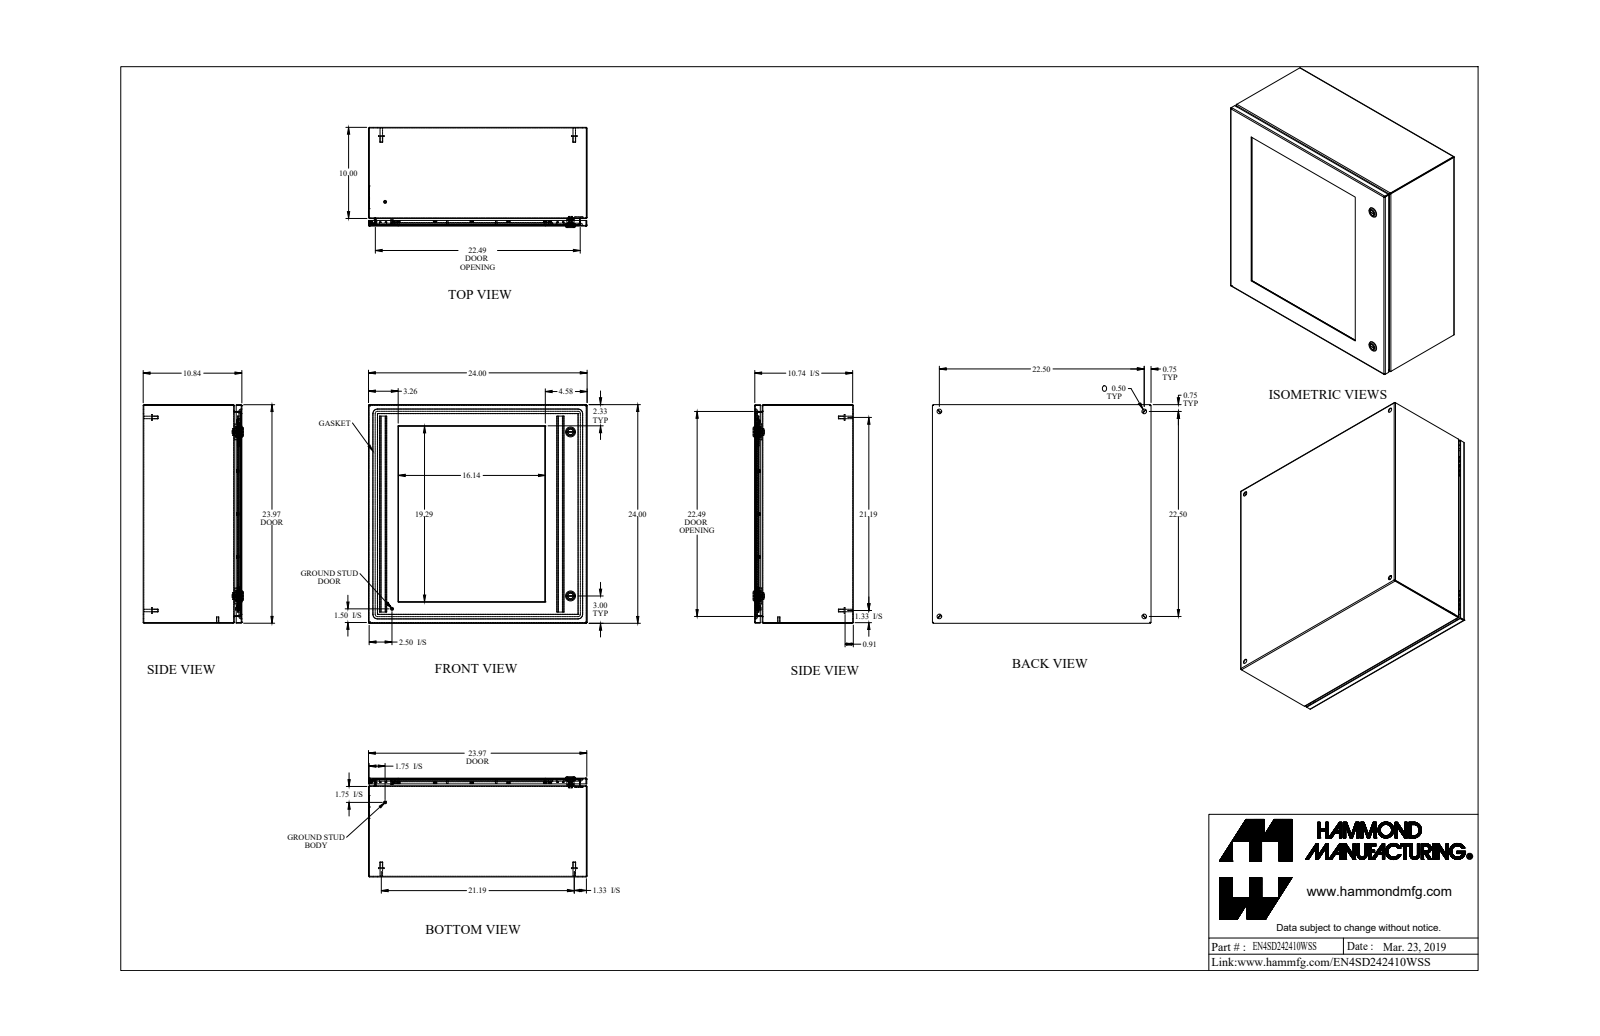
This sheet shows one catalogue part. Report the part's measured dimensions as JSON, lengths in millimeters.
{"part_name": "EN4SD242410WSS", "step_written_by": "SolidWorks 2019 (AUTOMOTIVE_DESIGN)", "units": "millimeters", "bodies": {"solids": 76, "faces": 1538, "planar": 792, "cylindrical": 466, "other": 280}, "overall_size": [609.6, 609.6, 279.3], "volume_mm3": 4008000, "surface_area_mm2": 3405000, "round_holes": [[3.3, 20], [6.4, 18], [12.7, 6], [5, 2], [9.8, 2], [16, 2], [19.5, 2], [4.4, 1], [6.1, 1], [6.1, 1]], "round_bosses_or_shafts": [[9.3, 20], [5.7, 19], [4.2, 18], [15.9, 6], [8, 6], [7, 4], [27.9, 2], [19.9, 2]], "partial_cylinders_radius": [[0.9, 16], [2.7, 16], [6.4, 16], [0.3, 12], [1.2, 12], [3.2, 12], [2.5, 8], [0.2, 4]], "face_to_face_distances": [1.8, 607.8, 273.4, 271.6, 605.9, 609.6, 265.3, 6.4, 267.1, 8.2], "hole_center_spacings": [451.6, 119.9, 136.4, 497.1, 534.2, 239.7, 359.6, 435.5]}
